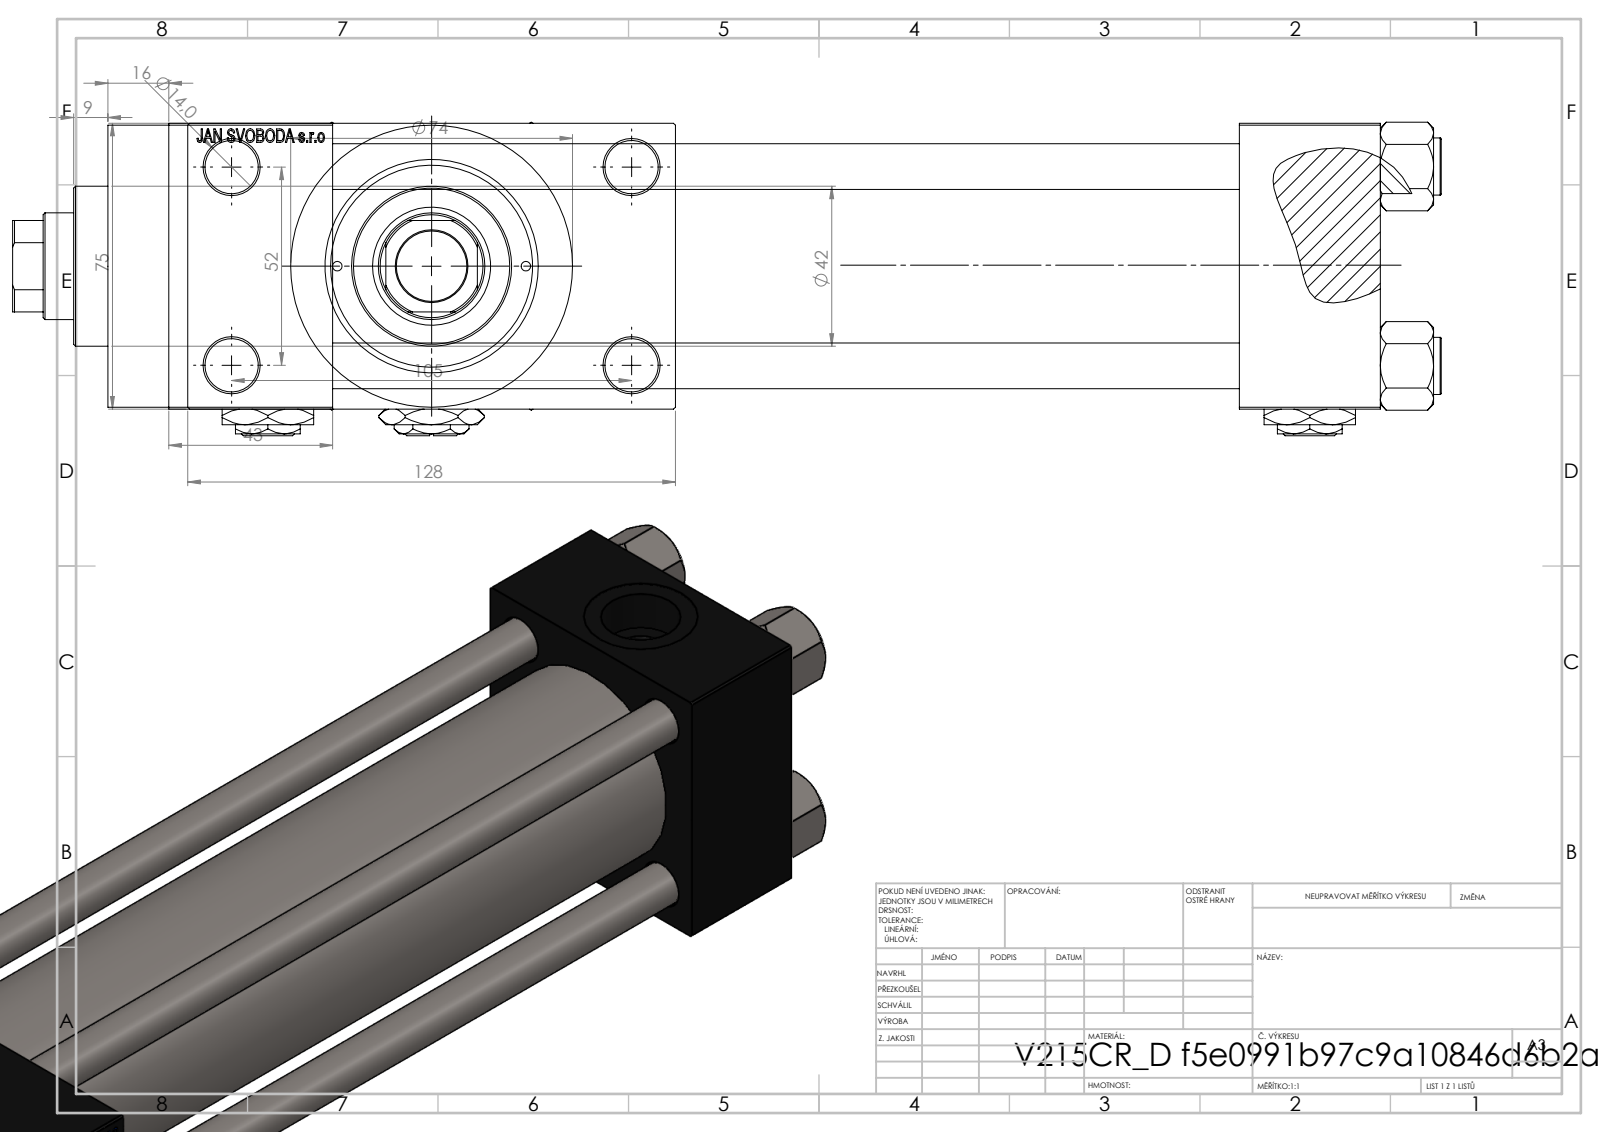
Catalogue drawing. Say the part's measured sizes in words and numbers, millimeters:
The part is named "NUT_M5_D; V215CR_VCP_D; Zatka_pro_OIL_PORT; V215CR_D_TYCINKA (+2 more)". Its 3-D file was written by "SolidWorks 2019 (CONFIG_CONTROL_DESIGN)". It is 13 solids with 1213 faces: 547 planar, 104 cylindrical and 562 other. Overall it measures 375 by 128 by 82.27 millimeters. Its volume is 1 093 000 cubic millimeters and its surface area 275 958 square millimeters. Round holes: 4 of diameter 12, 4 of diameter 14, 2 of diameter 2.5, 2 of diameter 7, 2 of diameter 20.96, 2 of diameter 30, 1 of diameter 18.5, 1 of diameter 28, 1 of diameter 31, 1 of diameter 41, 1 of diameter 50, 1 of diameter 53. Round bosses or shafts: 4 of diameter 15, 1 of diameter 74, 1 of diameter 56, 1 of diameter 42. Partial cylindrical surfaces (rounded edges, fillets, slot ends): 1 of radius 13.5. The main face-to-face distances are 75, 238, 37, 275, 26.5, 101.5, 318, 281, 43, 16. The hole center spacings are 26.19, 26.35, 36.98, 38.03, 52.3, 57.22, 58.43, 58.59.
